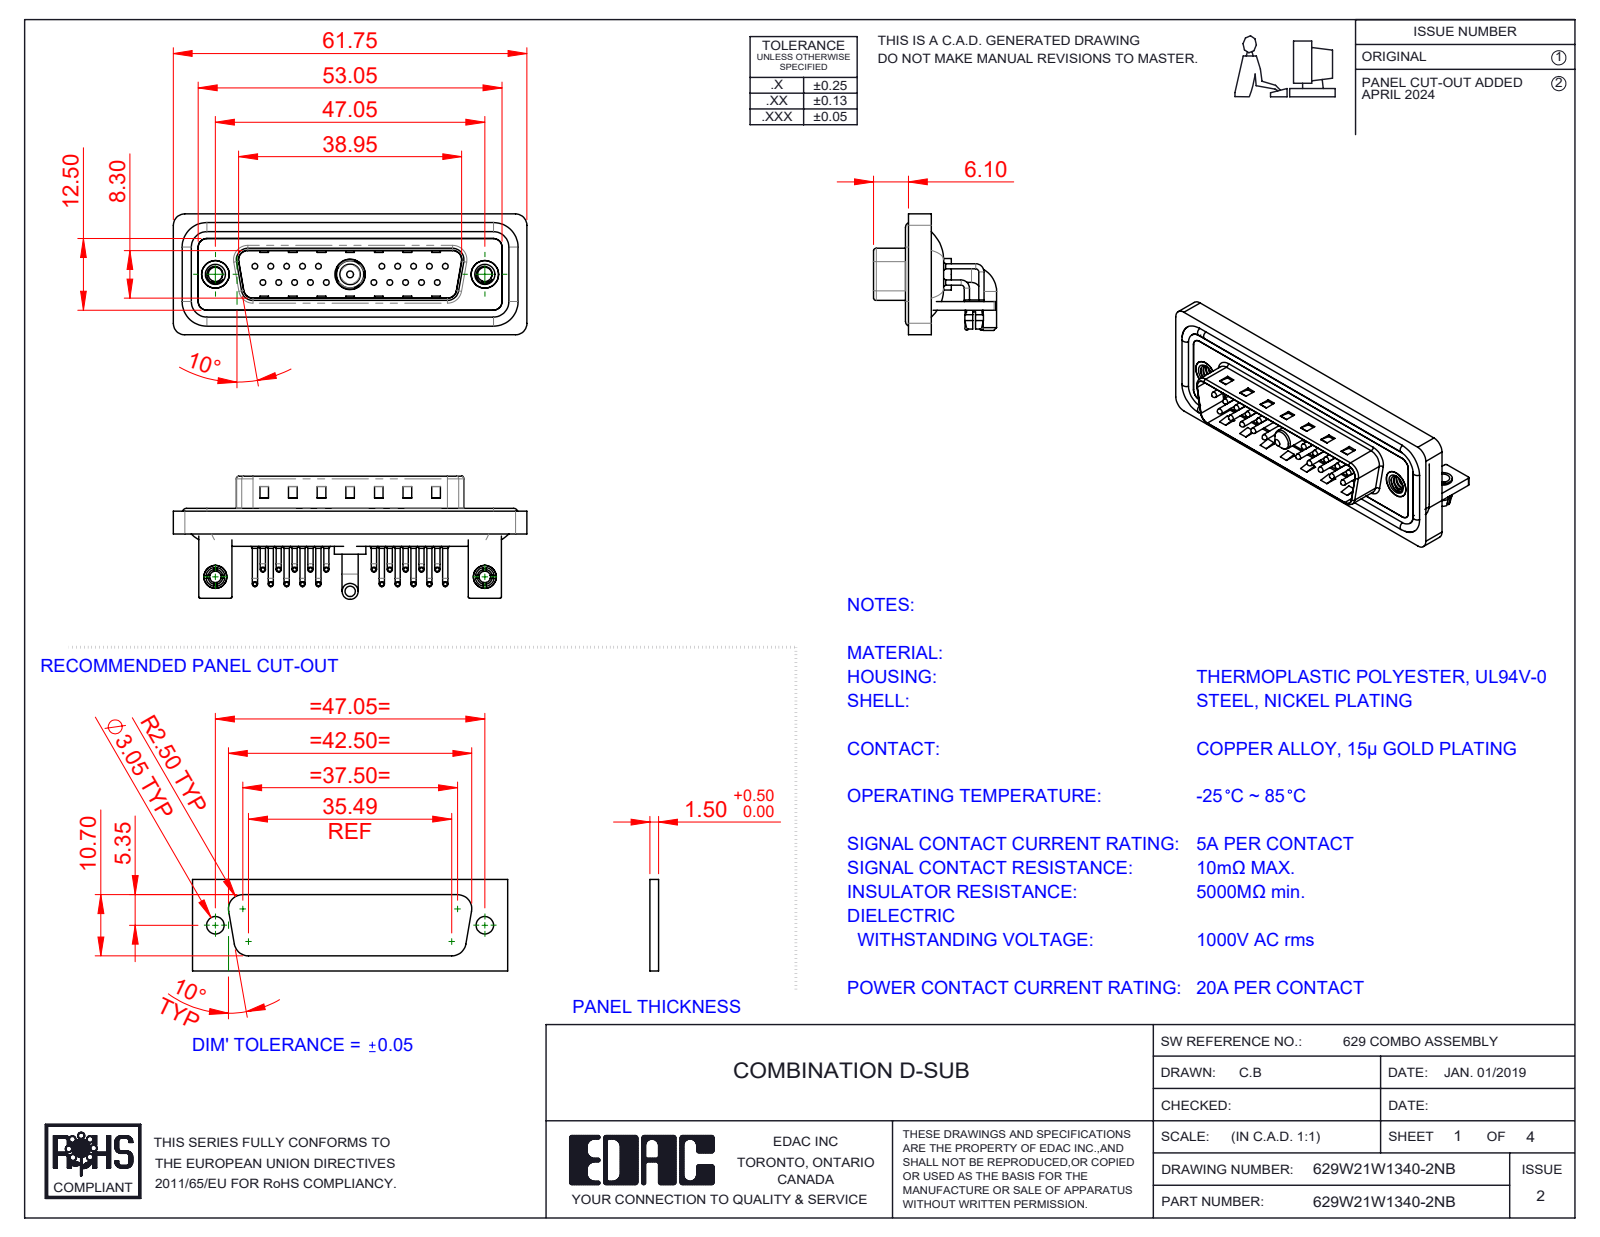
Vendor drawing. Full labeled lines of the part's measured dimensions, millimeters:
Part name (STEP PRODUCT): 629Combo Board Lock; 629Combo Housing_21W1; 629Combo Contact Row 2; 629Combo Waterproof Housing_25 Contacts (+7 more)
STEP written by: SolidWorks 2023 (CONFIG_CONTROL_DESIGN)
Units: millimetres
Bodies: 33 solids, 2856 faces (1567 planar, 979 cylindrical, 310 other)
Overall size (bounding box): 61.75 × 21.5 × 21.1
Volume: 7 726 mm³ · Surface area: 13 519 mm²
Round holes (diameter × count): ⌀2 ×22, ⌀0.75 ×20, ⌀1.6 ×20, ⌀2.5 ×4, ⌀3.2 ×2, ⌀4 ×2, ⌀4.8 ×2, ⌀5 ×2, ⌀4.85 ×1, ⌀5.3 ×1
Round bosses / shafts (diameter × count): ⌀0.9 ×40, ⌀1.5 ×20, ⌀1 ×20, ⌀0.65 ×20, ⌀1.6 ×4, ⌀4.9 ×2, ⌀4 ×2, ⌀3.4 ×2
Partial cylindrical surfaces — rounded edges, fillets, slot ends (radius × count): R1.01 ×20, R2 ×19, R1.5 ×18, R0.25 ×16, R0.5 ×9, R1.6 ×8, R0.6 ×4, R0.65 ×4
Main face-to-face distances: 0.4, 0.8, 2.1, 2.9, 1.5, 1.1, 4.1, 1.6, 4.5, 3.7
Hole centre spacings: 3.16, 2.77, 5.54, 8.31, 5.04, 19.39, 20.97, 22.16
